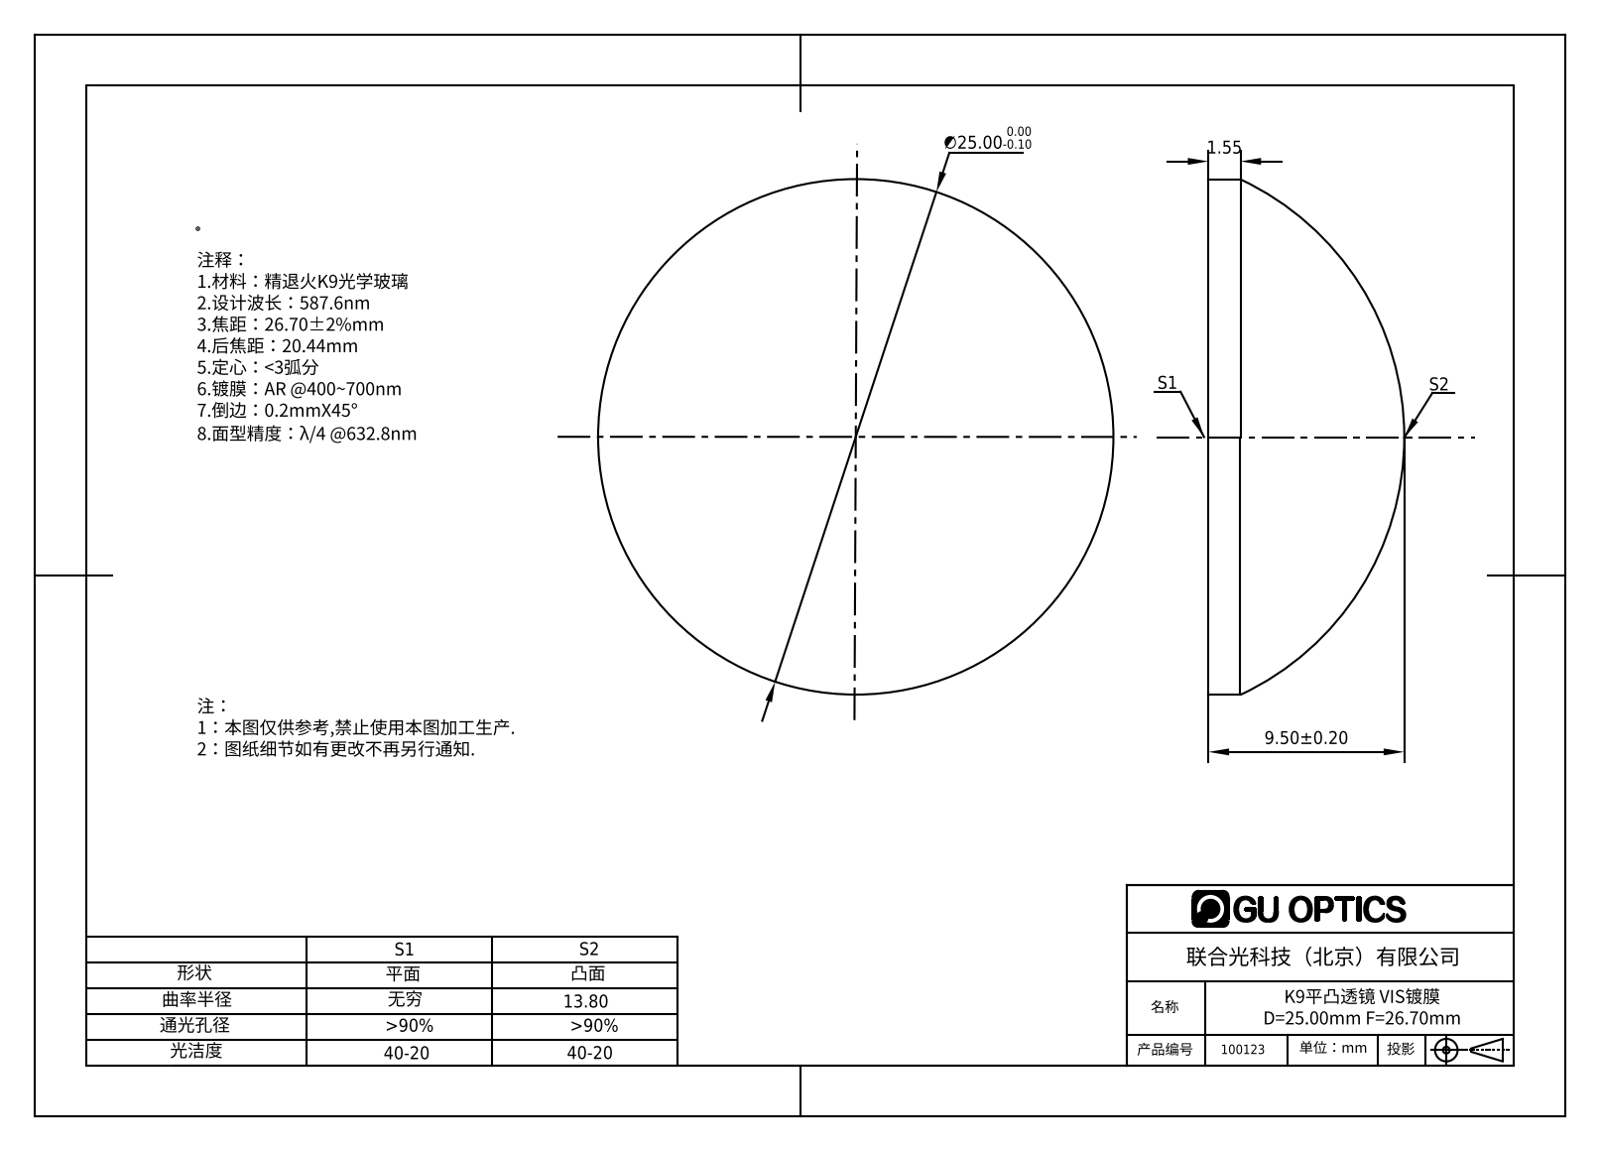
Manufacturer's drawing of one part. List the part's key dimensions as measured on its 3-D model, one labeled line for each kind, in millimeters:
Part name (STEP PRODUCT): 100123
STEP written by: SolidWorks 2016 (AUTOMOTIVE_DESIGN)
Units: millimetres
Bodies: 1 solid, 5 faces (1 planar, 2 cylindrical, 2 other)
Overall size (bounding box): 25 × 25 × 9.5
Volume: 2 989 mm³ · Surface area: 1 305 mm²
Round bosses / shafts (diameter × count): ⌀25 ×1
